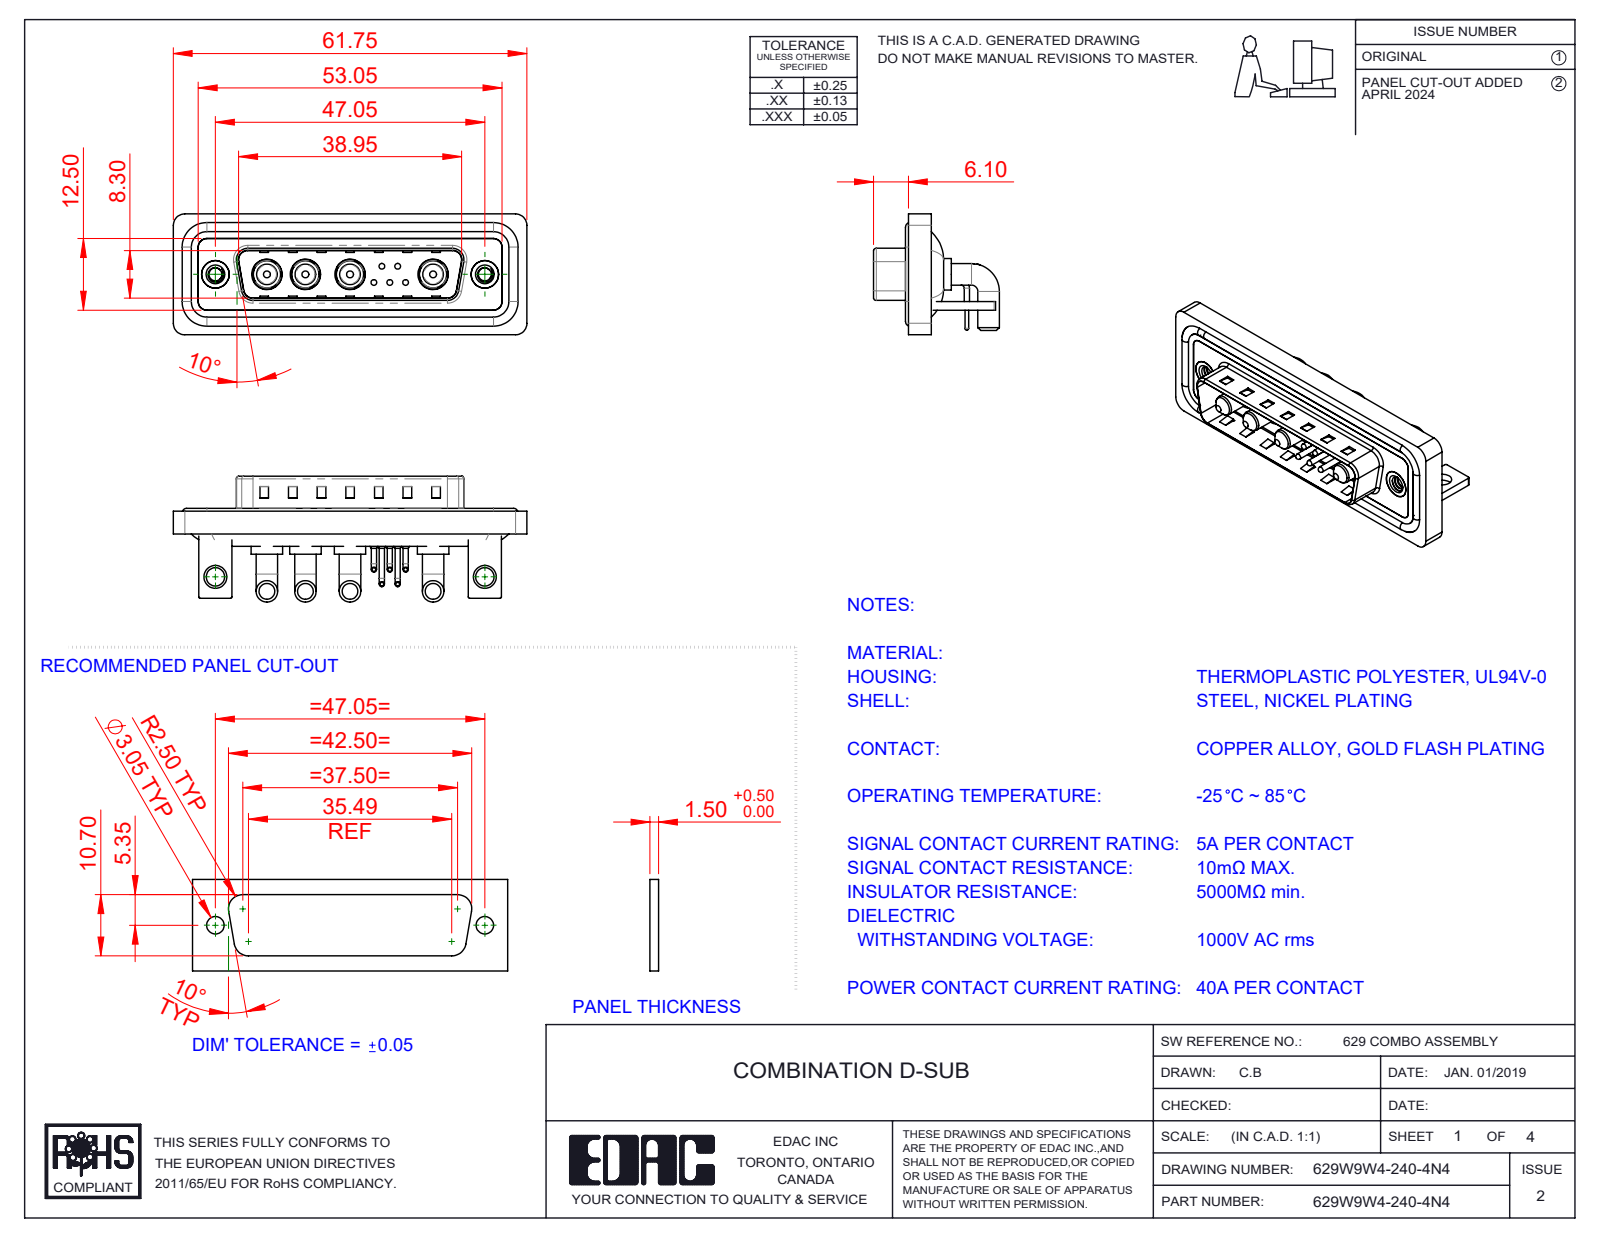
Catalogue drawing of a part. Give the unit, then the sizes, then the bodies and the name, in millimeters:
Units: millimetres
Overall size (bounding box): 61.75 × 21.98 × 21.1
Round holes (diameter × count): ⌀0.75 ×5, ⌀1.6 ×5, ⌀2 ×5, ⌀4.85 ×4, ⌀5.3 ×4, ⌀2.26 ×2, ⌀3.2 ×2, ⌀4 ×2, ⌀4.8 ×2, ⌀5 ×2
Round bosses / shafts (diameter × count): ⌀0.9 ×10, ⌀3.75 ×8, ⌀1.5 ×5, ⌀1 ×5, ⌀0.65 ×5, ⌀5.5 ×4, ⌀5.2 ×4, ⌀4.75 ×4
Partial cylindrical surfaces — rounded edges, fillets, slot ends (radius × count): R2 ×19, R1.5 ×18, R0.25 ×16, R0.5 ×9, R1.6 ×8, R1.01 ×5, R0.6 ×4, R0.65 ×4
Main face-to-face distances: 0.4, 1.5, 0.8, 2.9, 2.1, 1.1, 3.7, 4.1, 4.5, 1.6
Hole centre spacings: 3.16, 2.77, 5.04, 14.5, 47.05, 2.78, 4.4, 4.41
Volume: 8 274 mm³ · Surface area: 13 139 mm²
Bodies: 22 solids, 1245 faces (589 planar, 470 cylindrical, 186 other)
Part name (STEP PRODUCT): 629Combo Threaded Rivet_3; 629Combo Shell Rear_25 Contacts; 629Combo Waterproof Housing_25 Contacts; Power Pin_40A RA (+6 more)
STEP written by: SolidWorks 2023 (CONFIG_CONTROL_DESIGN)
